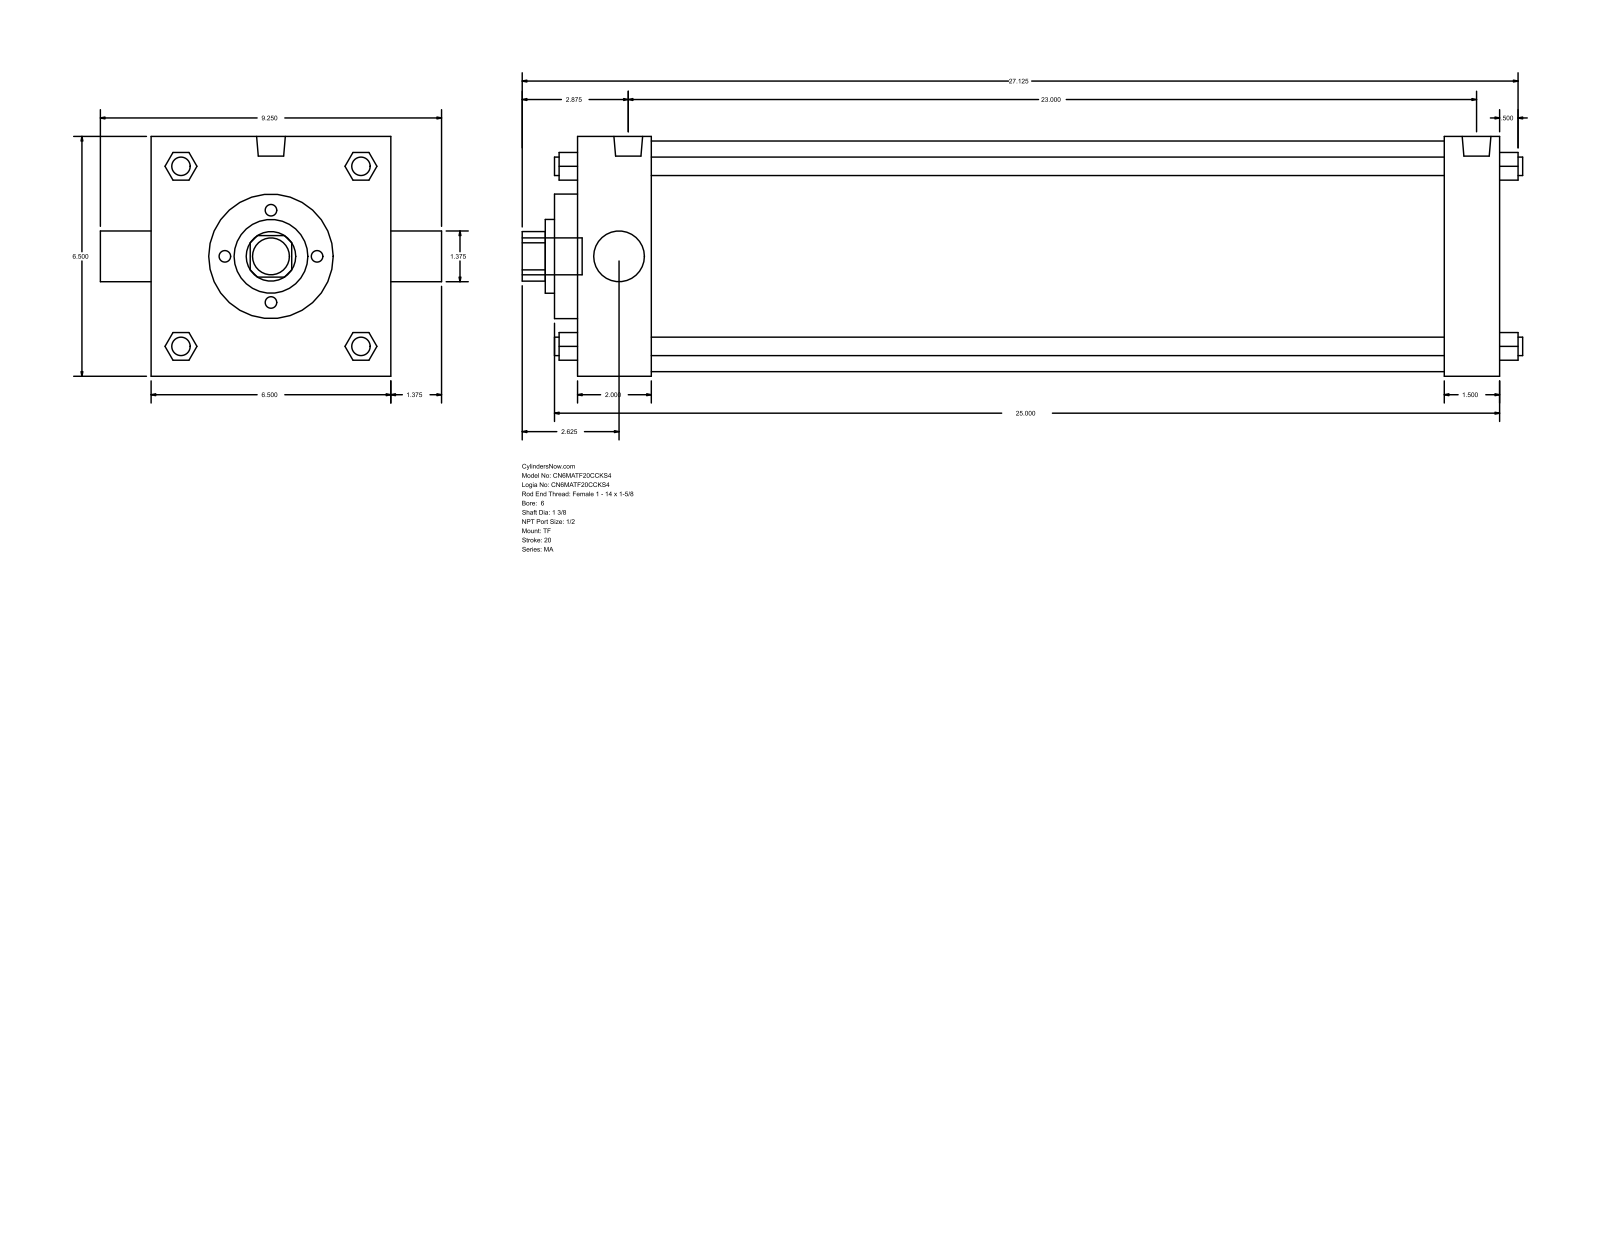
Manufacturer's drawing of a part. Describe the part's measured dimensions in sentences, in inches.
The part is named "MA_TF__0600_1.375". Its 3-D file was written by "GSSL Pune (CONFIG_CONTROL_DESIGN)". It is 0 solids with 122 faces: 93 planar, 29 cylindrical and 0 other. Overall it measures 27.125 by 9.25 by 6.5 inches. Round holes: 2 of diameter 1.375, 1 of diameter 2, 1 of diameter 3.375, 1 of diameter 6.25. Round bosses or shafts: 4 of diameter 0.5, 3 of diameter 0.687, 2 of diameter 0.778, 1 of diameter 1. Partial cylindrical surfaces (rounded edges, fillets, slot ends): 1 of radius 0.672. The main face-to-face distances are 6.5, 25.125, 1.5, 2, 23.125, 23.625, 21.625, 0.625, 2.625, 24.25.
